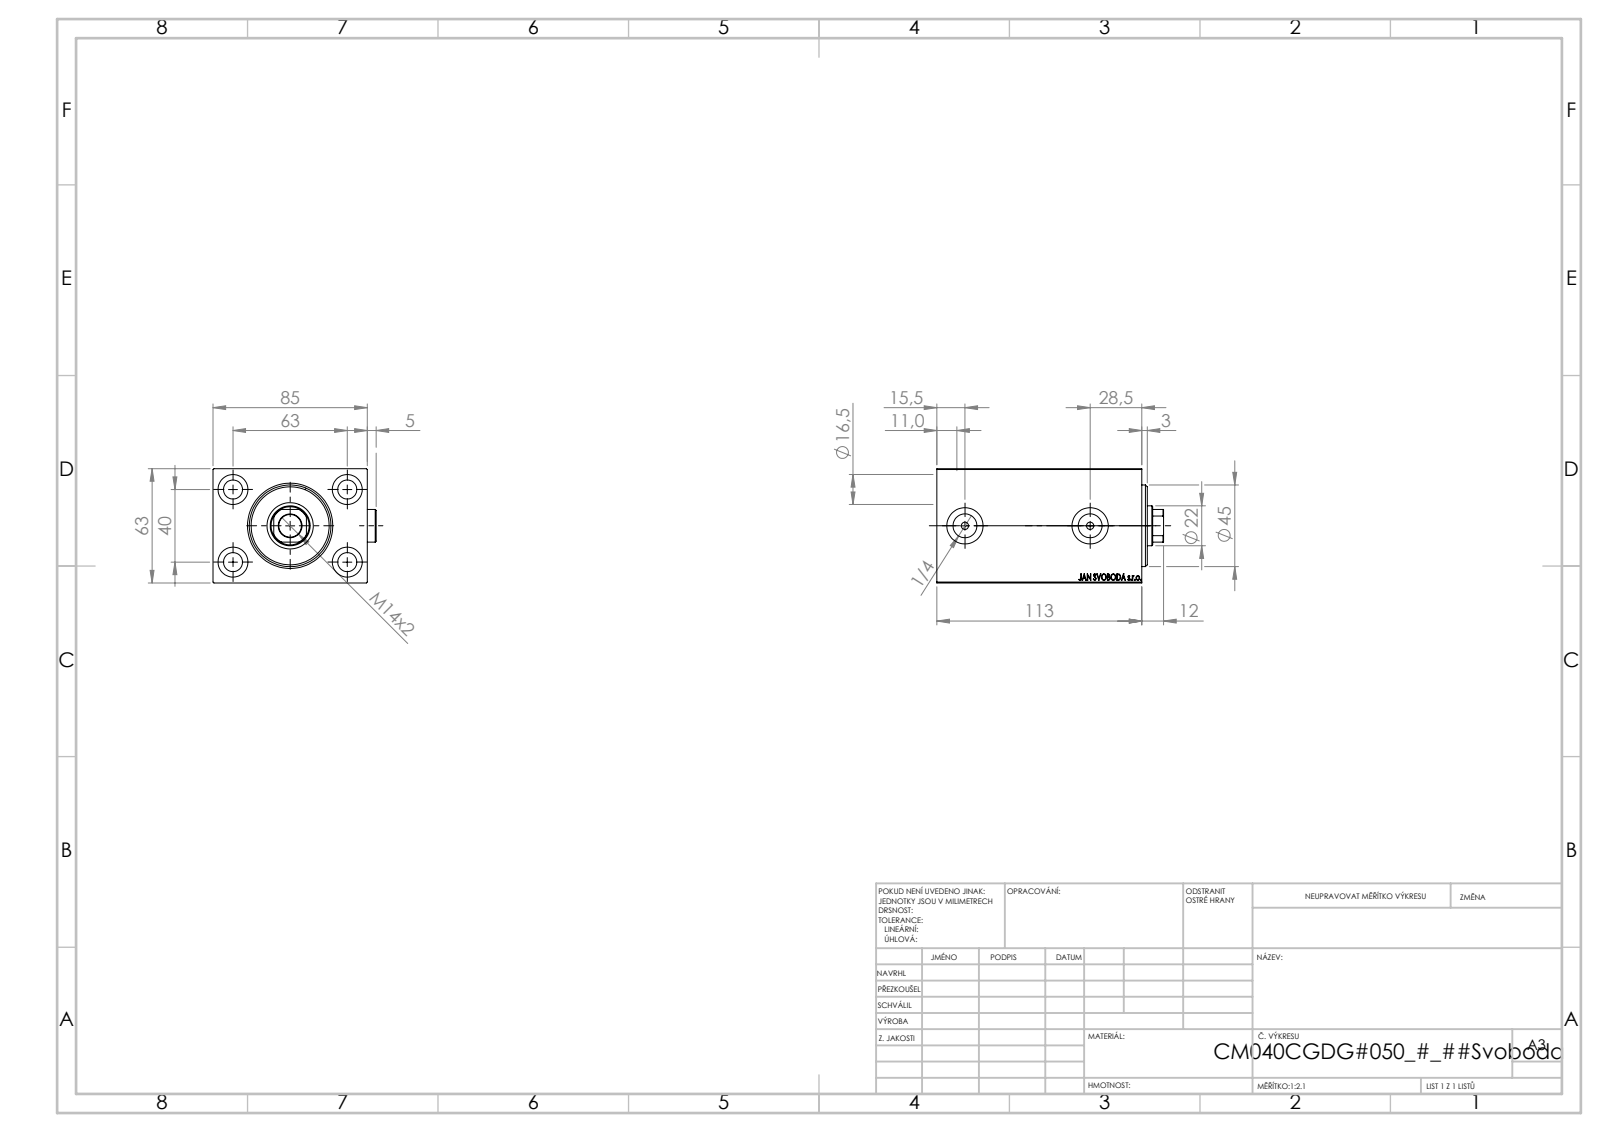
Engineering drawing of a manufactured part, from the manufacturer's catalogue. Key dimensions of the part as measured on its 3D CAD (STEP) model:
Part name (STEP PRODUCT): V450CM_VC_B; V450CM_C_Body; Zatka_OIL_PORT; V450CM_C_VCP
STEP written by: SolidWorks 2019 (CONFIG_CONTROL_DESIGN)
Units: millimetres
Bodies: 5 solids, 916 faces (442 planar, 76 cylindrical, 398 other)
Overall size (bounding box): 125 × 89.9 × 63
Volume: 510 419 mm³ · Surface area: 95 677 mm²
Round holes (diameter × count): ⌀10.5 ×4, ⌀16.5 ×4, ⌀4 ×2, ⌀13.16 ×2, ⌀20 ×2, ⌀12.5 ×1, ⌀22 ×1, ⌀25.5 ×1, ⌀40 ×1, ⌀42 ×1, ⌀45 ×1
Round bosses / shafts (diameter × count): ⌀18 ×2
Partial cylindrical surfaces — rounded edges, fillets, slot ends (radius × count): R10.5 ×1
Main face-to-face distances: 63, 85, 12, 101, 113, 51, 84.9, 89, 11, 3
Hole centre spacings: 37.31, 40, 63, 74.63, 69
